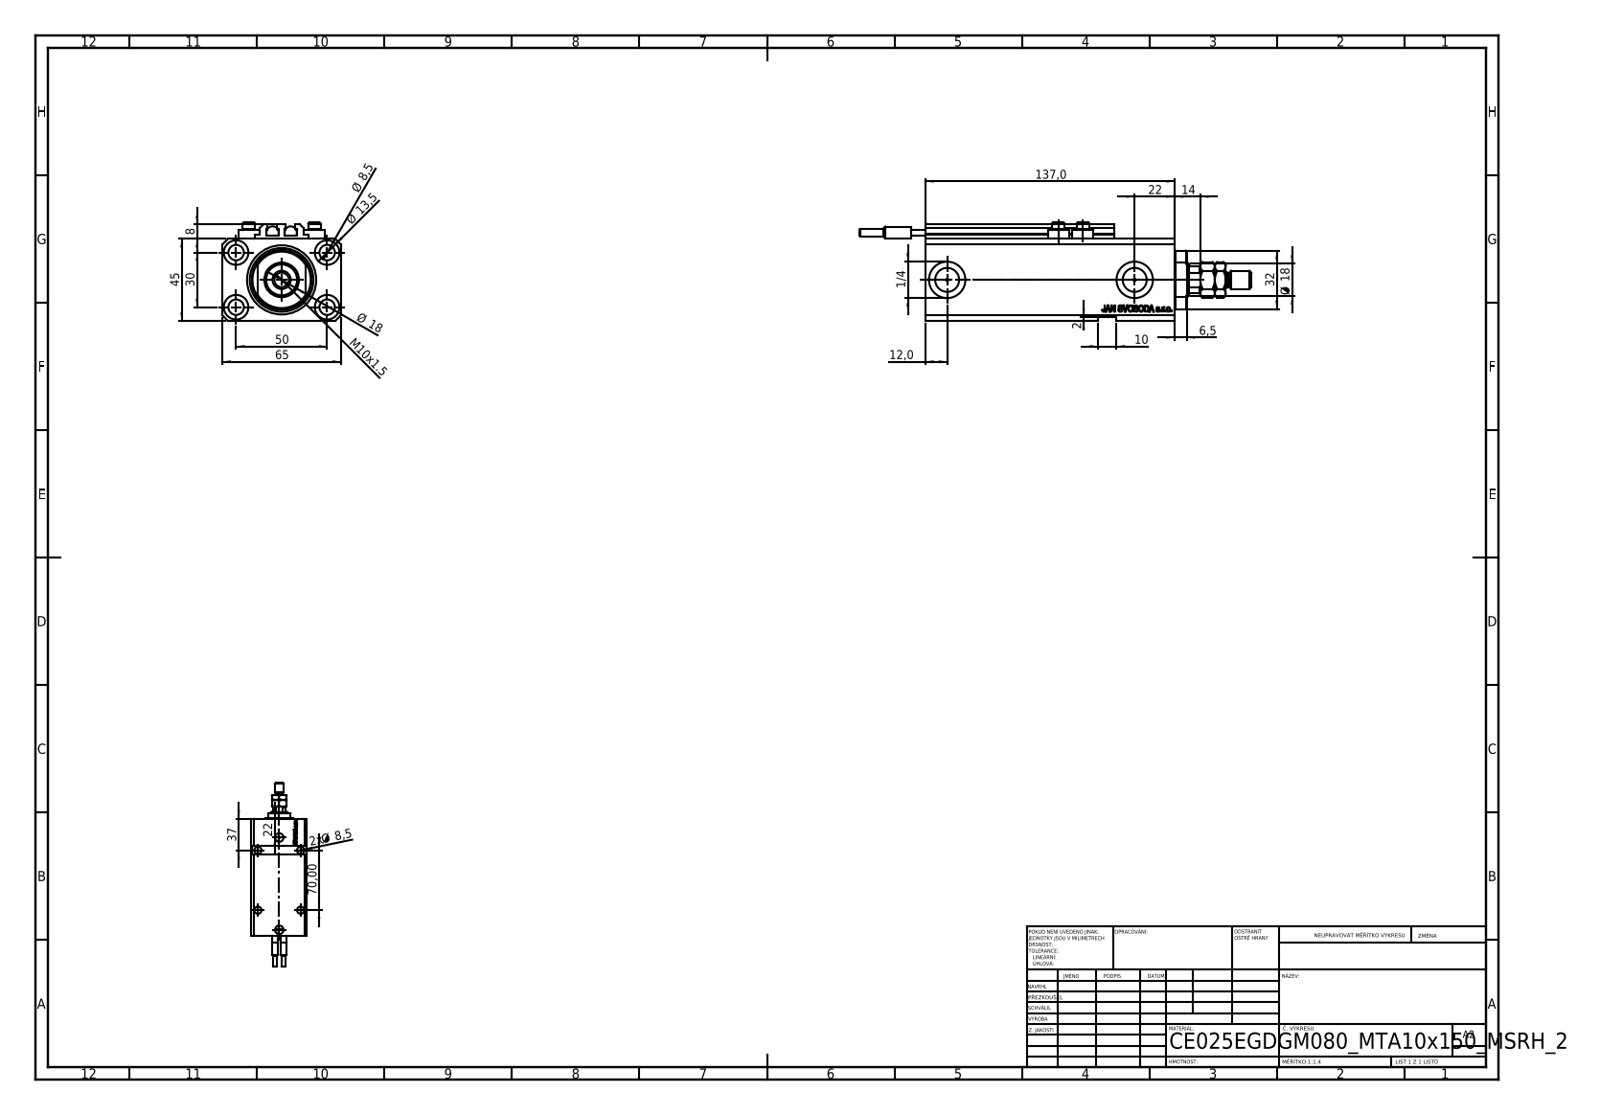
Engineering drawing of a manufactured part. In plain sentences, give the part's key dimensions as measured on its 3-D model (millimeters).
The part is named "ALLEN BOLT V250CE; MTA; V250CE_C_VCP; V250CE_E_Body (+2 more)". Its 3-D file was written by "SolidWorks 2019 (CONFIG_CONTROL_DESIGN)". It is 11 solids with 1204 faces: 562 planar, 174 cylindrical and 468 other. Overall it measures 215 by 65 by 54 millimeters. Its volume is 354 936 cubic millimeters and its surface area 99 171 square millimeters. Round holes: 9 of diameter 8.5, 4 of diameter 1.25, 4 of diameter 4, 4 of diameter 13.5, 2 of diameter 10, 2 of diameter 13.16, 2 of diameter 20, 1 of diameter 18, 1 of diameter 25, 1 of diameter 38. Round bosses or shafts: 4 of diameter 11.6, 4 of diameter 7, 2 of diameter 6.8, 2 of diameter 6.5, 2 of diameter 4, 1 of diameter 10, 1 of diameter 8. Partial cylindrical surfaces (rounded edges, fillets, slot ends): 10 of radius 0.2, 1 of radius 8.5, 1 of radius 16. The main face-to-face distances are 45, 65, 47, 2, 14, 2.5, 10, 3, 123, 24. The hole center spacings are 29.15, 50, 13.6, 15.12, 27.89, 30, 33.61, 33.62.
